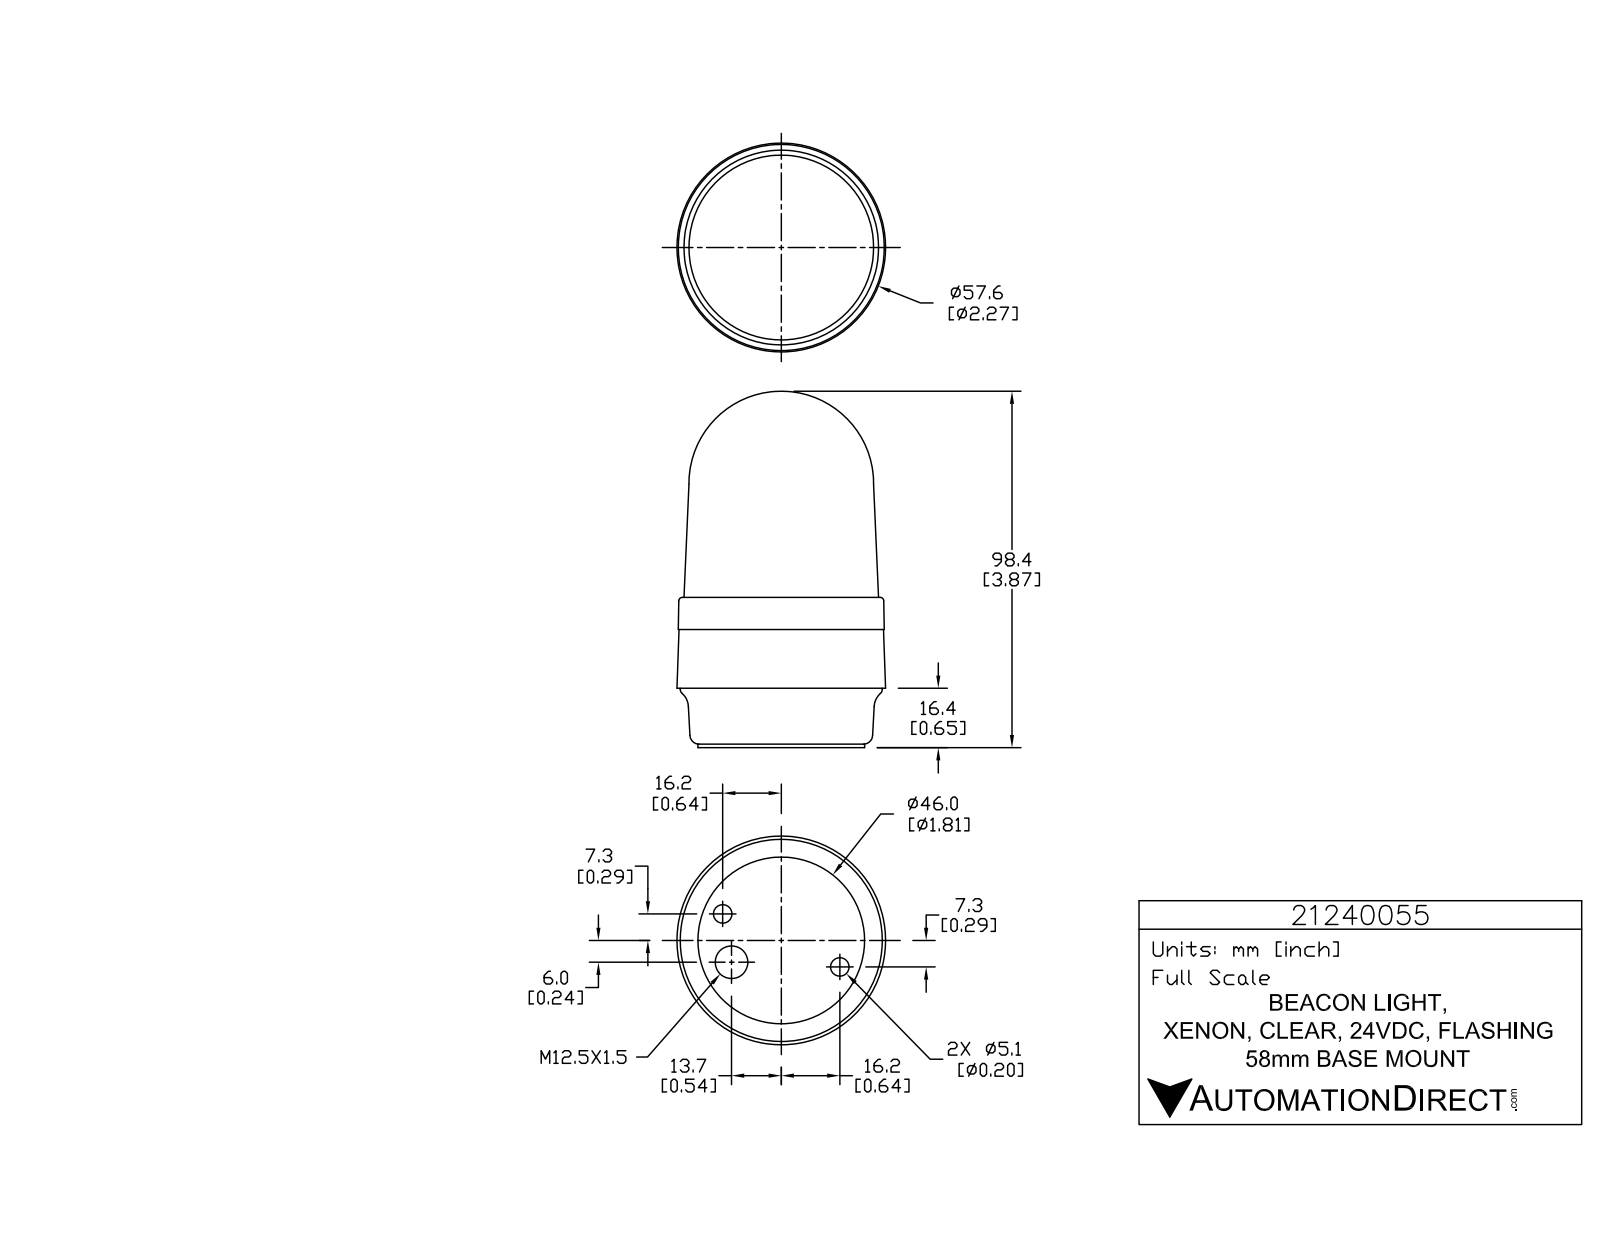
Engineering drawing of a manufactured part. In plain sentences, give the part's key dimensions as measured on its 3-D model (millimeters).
The part is named "21240055". Its 3-D file was written by "SolidWorks 2015 (AUTOMOTIVE_DESIGN)". It is 1 solid with 764 faces: 527 planar, 145 cylindrical and 92 other. Overall it measures 98.4 by 57.63 by 57.63 millimeters. Its volume is 199 898 cubic millimeters and its surface area 18 922 square millimeters. Round holes: 3 of diameter 0.99, 2 of diameter 5.11, 1 of diameter 9. Round bosses or shafts: 3 of diameter 5.74, 3 of diameter 1.43, 1 of diameter 55.8, 1 of diameter 46. Partial cylindrical surfaces (rounded edges, fillets, slot ends): 6 of radius 0.2, 6 of radius 0.21, 6 of radius 0.21, 6 of radius 3.32, 3 of radius 0.1, 3 of radius 0.12, 3 of radius 0.19, 3 of radius 0.2. The main face-to-face distances are 16.4, 1, 15.4, 41.5, 40.5, 25.1, 32.6, 31.6, 16.2, 8.9. The hole center spacings are 13.56, 29.94, 35.5.
